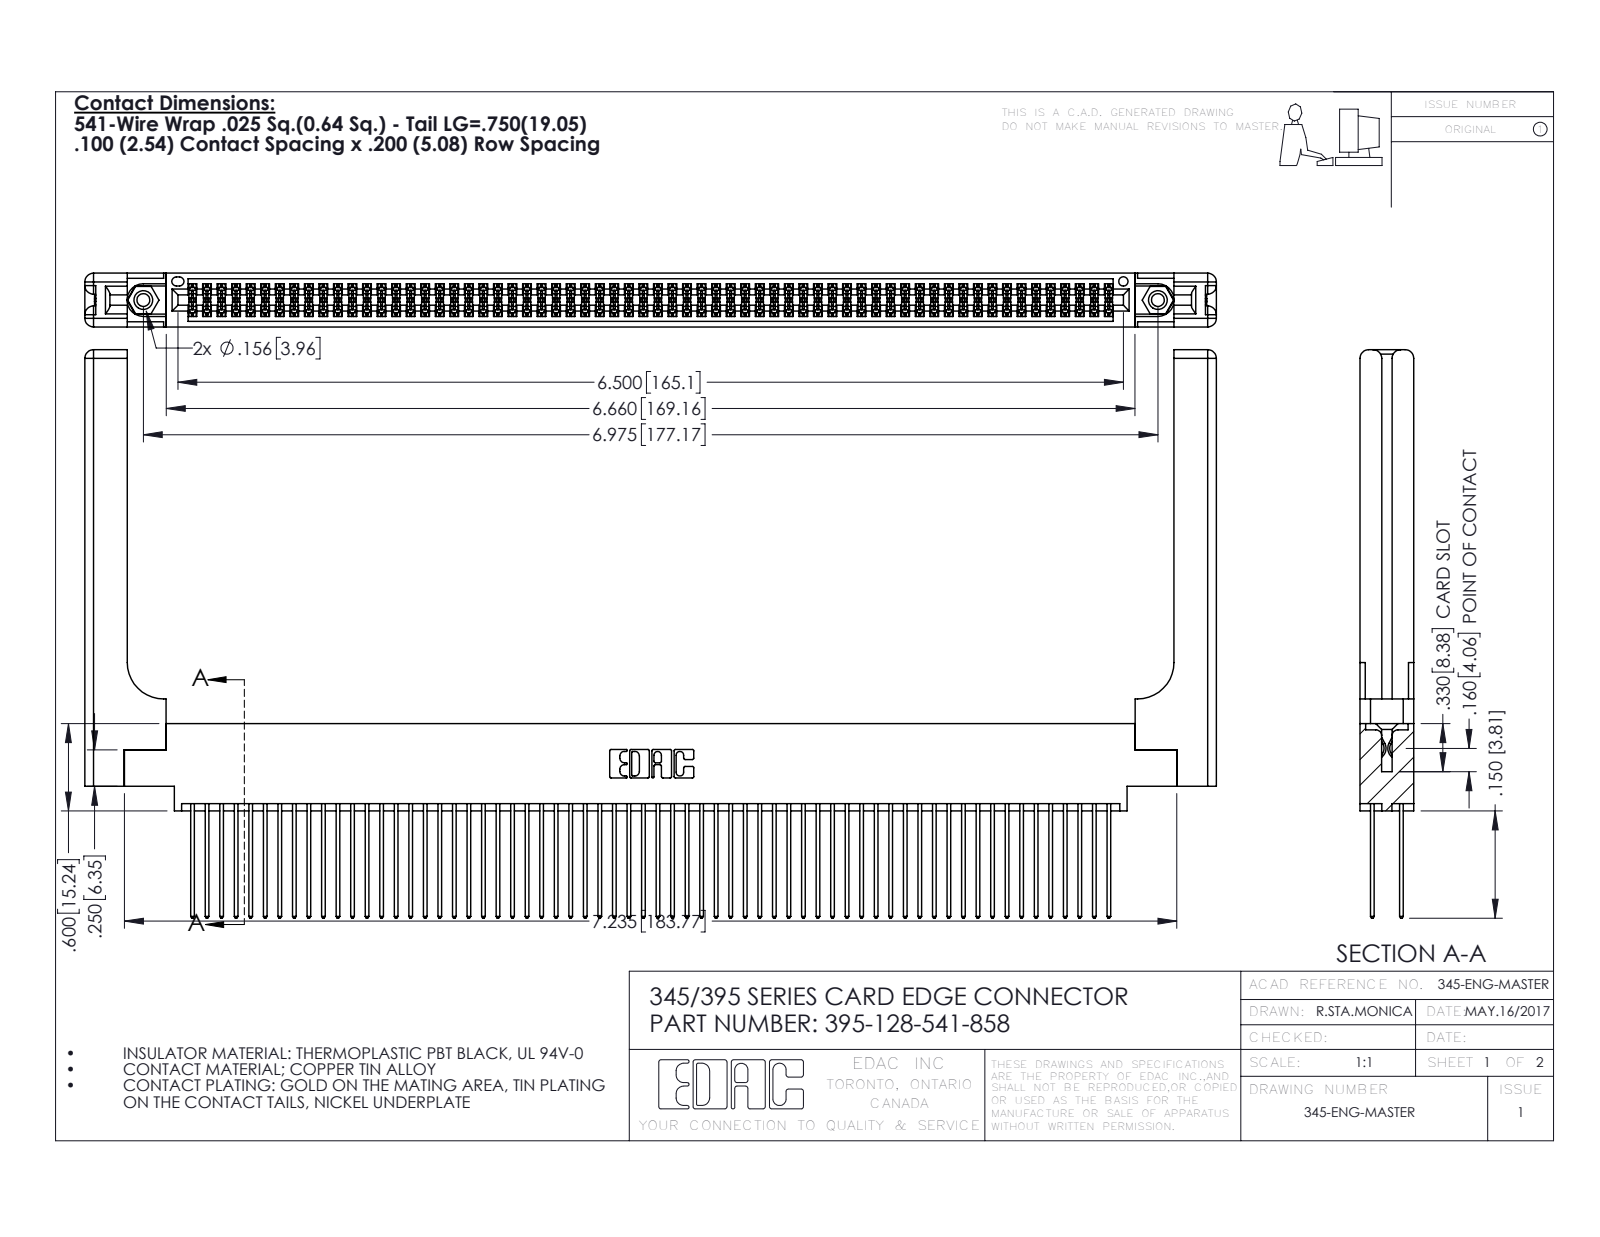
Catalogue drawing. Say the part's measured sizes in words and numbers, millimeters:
The part is named "345-220-058_345-220-058; 345-250-001_345-250-001-102; 345 Part_0.170 Offset - 0.156 Dia-TH; 345-292-001_345-293-141 (+1 more)". Its 3-D file was written by "SolidWorks 2016 (CONFIG_CONTROL_DESIGN)". It is 133 solids with 6786 faces: 4456 planar, 2270 cylindrical and 60 other. Overall it measures 197.6 by 99.2 by 9.4 millimeters. Its volume is 28 500 cubic millimeters and its surface area 38 670 square millimeters. Round holes: 2 of diameter 2.3, 2 of diameter 3.2, 2 of diameter 4, 1 of diameter 1.6. Round bosses or shafts: 2 of diameter 3.9. Partial cylindrical surfaces (rounded edges, fillets, slot ends): 192 of radius 0.2, 128 of radius 0.3, 22 of radius 0.3, 16 of radius 1.5, 6 of radius 0.2, 6 of radius 0.8, 3 of radius 0.7, 2 of radius 0.4. The main face-to-face distances are 1.8, 7.6, 2.5, 6.9, 0.6, 5.1, 9.4, 5.7, 4.4, 3.8. The hole center spacings are 6.9, 171.2, 177.2.
